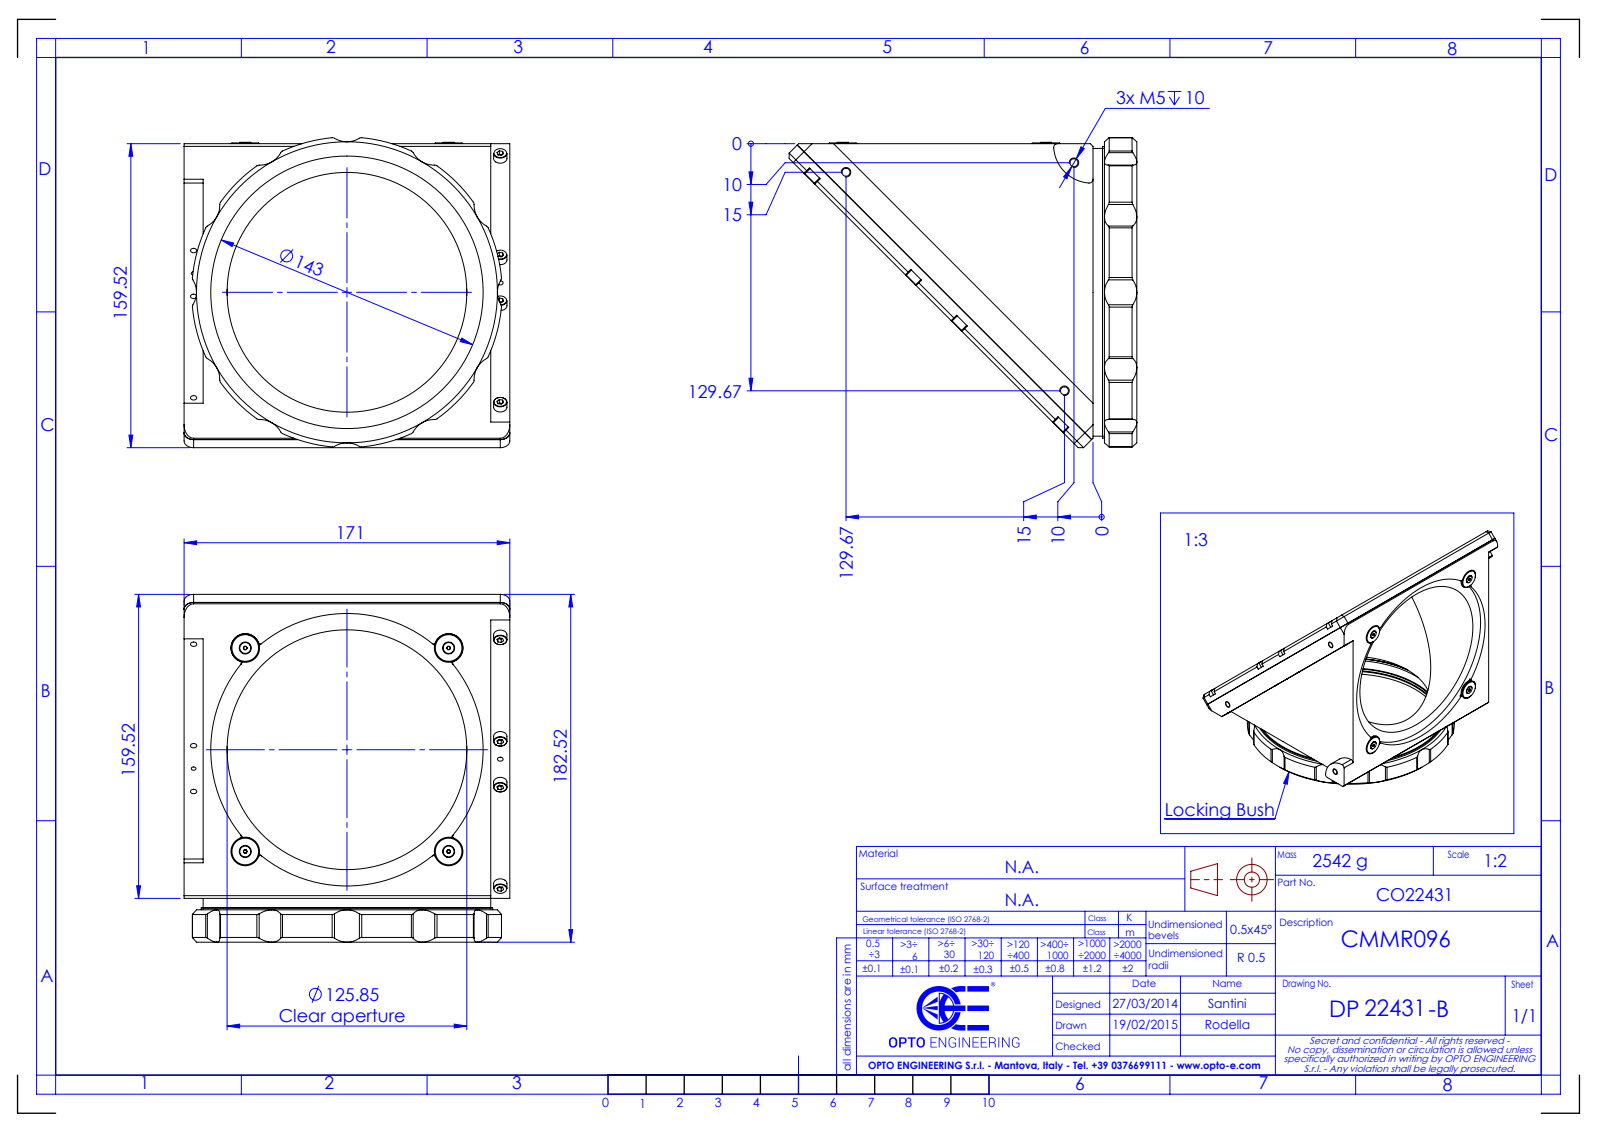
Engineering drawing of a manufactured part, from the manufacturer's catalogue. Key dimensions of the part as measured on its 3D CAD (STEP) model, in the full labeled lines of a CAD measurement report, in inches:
Part name (STEP PRODUCT): DP22431-B_CMMR096
STEP written by: SolidWorks 2021 (CONFIG_CONTROL_DESIGN)
Units: inches
Bodies: 0 solids, 394 faces (132 planar, 174 cylindrical, 88 other)
Overall size (bounding box): 7.186 × 6.732 × 6.404
Round holes (diameter × count): ⌀0.13 ×8, ⌀0.165 ×3, ⌀0.118 ×2, ⌀4.955 ×2, ⌀5.63 ×2, ⌀0.098 ×1, ⌀5.654 ×1, ⌀5.717 ×1, ⌀5.807 ×1, ⌀5.945 ×1, ⌀6.024 ×1
Round bosses / shafts (diameter × count): ⌀0.276 ×8, ⌀0.591 ×4, ⌀0.226 ×4
Partial cylindrical surfaces — rounded edges, fillets, slot ends (radius × count): R0.079 ×26, R0.492 ×12, R0.039 ×8, R0.157 ×4, R0.197 ×4, R0.787 ×1, R3.209 ×1
Main face-to-face distances: 0.315, 5.945, 0.394, 6.339, 0.197, 0.276, 0.906, 0.591, 0.15, 0.465
Hole centre spacings: 6.339, 0.669, 6.374, 6.998, 7.306, 1.339, 2.964, 2.965
